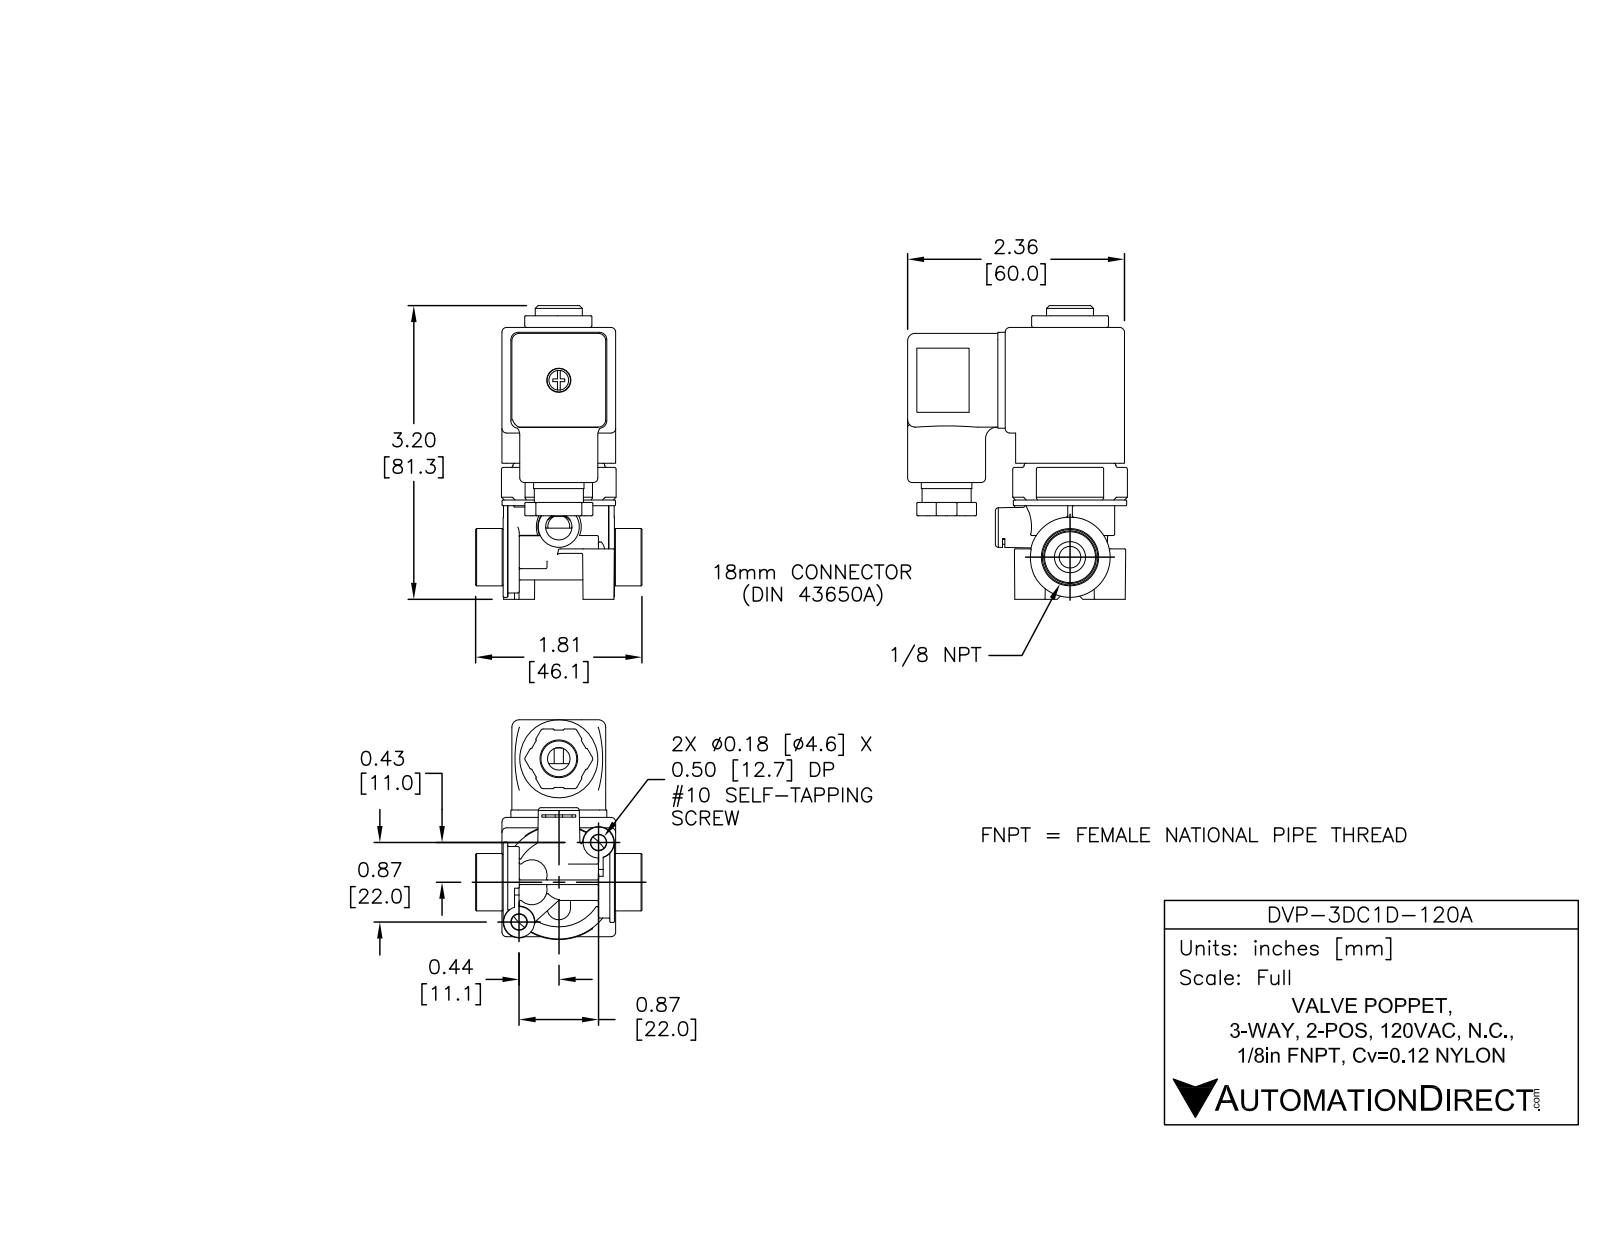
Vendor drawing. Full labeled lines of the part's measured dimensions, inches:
Part name (STEP PRODUCT): DVP-3DC1D-120A
STEP written by: SolidWorks 2015 (AUTOMOTIVE_DESIGN)
Units: inches
Bodies: 10 solids, 2067 faces (823 planar, 396 cylindrical, 848 other)
Overall size (bounding box): 3.204 × 2.395 × 1.813
Volume: 4.004 in³ · Surface area: 57.76 in²
Round holes (diameter × count): ⌀0.06 ×2, ⌀0.236 ×2, ⌀0.339 ×2, ⌀0.08 ×1, ⌀0.093 ×1, ⌀0.102 ×1, ⌀0.12 ×1, ⌀0.137 ×1, ⌀0.203 ×1, ⌀0.245 ×1, ⌀0.263 ×1, ⌀0.287 ×1
Round bosses / shafts (diameter × count): ⌀0.29 ×2, ⌀1.236 ×1, ⌀1 ×1, ⌀0.972 ×1, ⌀0.922 ×1, ⌀0.89 ×1, ⌀0.875 ×1, ⌀0.85 ×1
Partial cylindrical surfaces — rounded edges, fillets, slot ends (radius × count): R0.01 ×85, R0.015 ×50, R0.05 ×21, R0.02 ×12, R0.08 ×12, R0.026 ×6, R0.03 ×6, R0.04 ×4
Main face-to-face distances: 1.083, 1.24, 0.048, 0.157, 0.925, 1.48, 0.109, 1.131, 0.974, 1.367
Hole centre spacings: 0.281, 0.283, 1.062, 1.343, 1.345, 1.612, 1.626, 2.184
